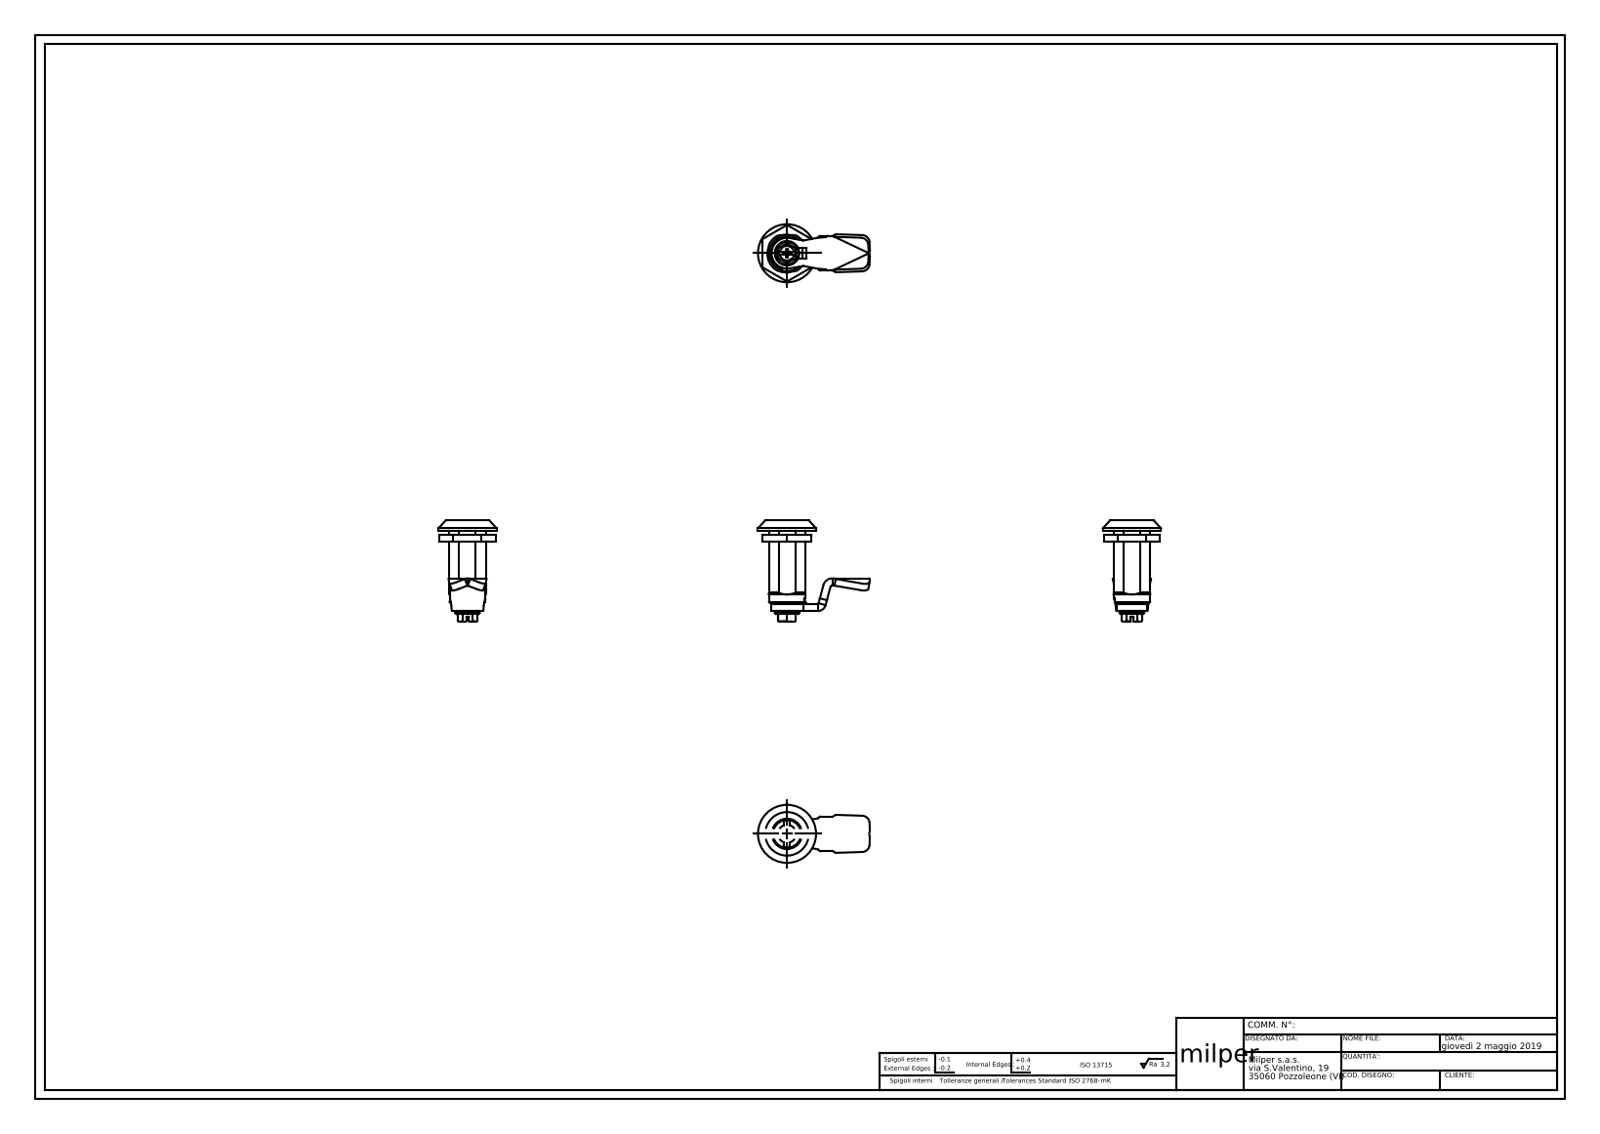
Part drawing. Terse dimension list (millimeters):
name: 1.26.21.0008-serratura-asportabili-15mm-Milper
written by: SolidWorks 2019 (CONFIG_CONTROL_DESIGN)
unit: mm
bodies: 0 solids, 680 faces (354 planar, 218 cylindrical, 108 other)
size: 114.47 × 65.64 × 32
holes: 1× ⌀5, 1× ⌀5.8, 1× ⌀6, 1× ⌀6.2, 1× ⌀8, 1× ⌀10, 1× ⌀12, 1× ⌀16.1, 1× ⌀20, 1× ⌀20.38
bosses: 1× ⌀32, 1× ⌀22, 1× ⌀19.8, 1× ⌀16, 1× ⌀13.5, 1× ⌀12.8, 1× ⌀9.9, 1× ⌀9
rounds: 30× R0.3, 29× R0.5, 8× R4, 7× R1, 2× R5, 2× R6, 2× R20.23, 1× R0.4
face distances: 4, 20, 38, 6, 7.23, 12.77, 14, 24, 40, 6.5
